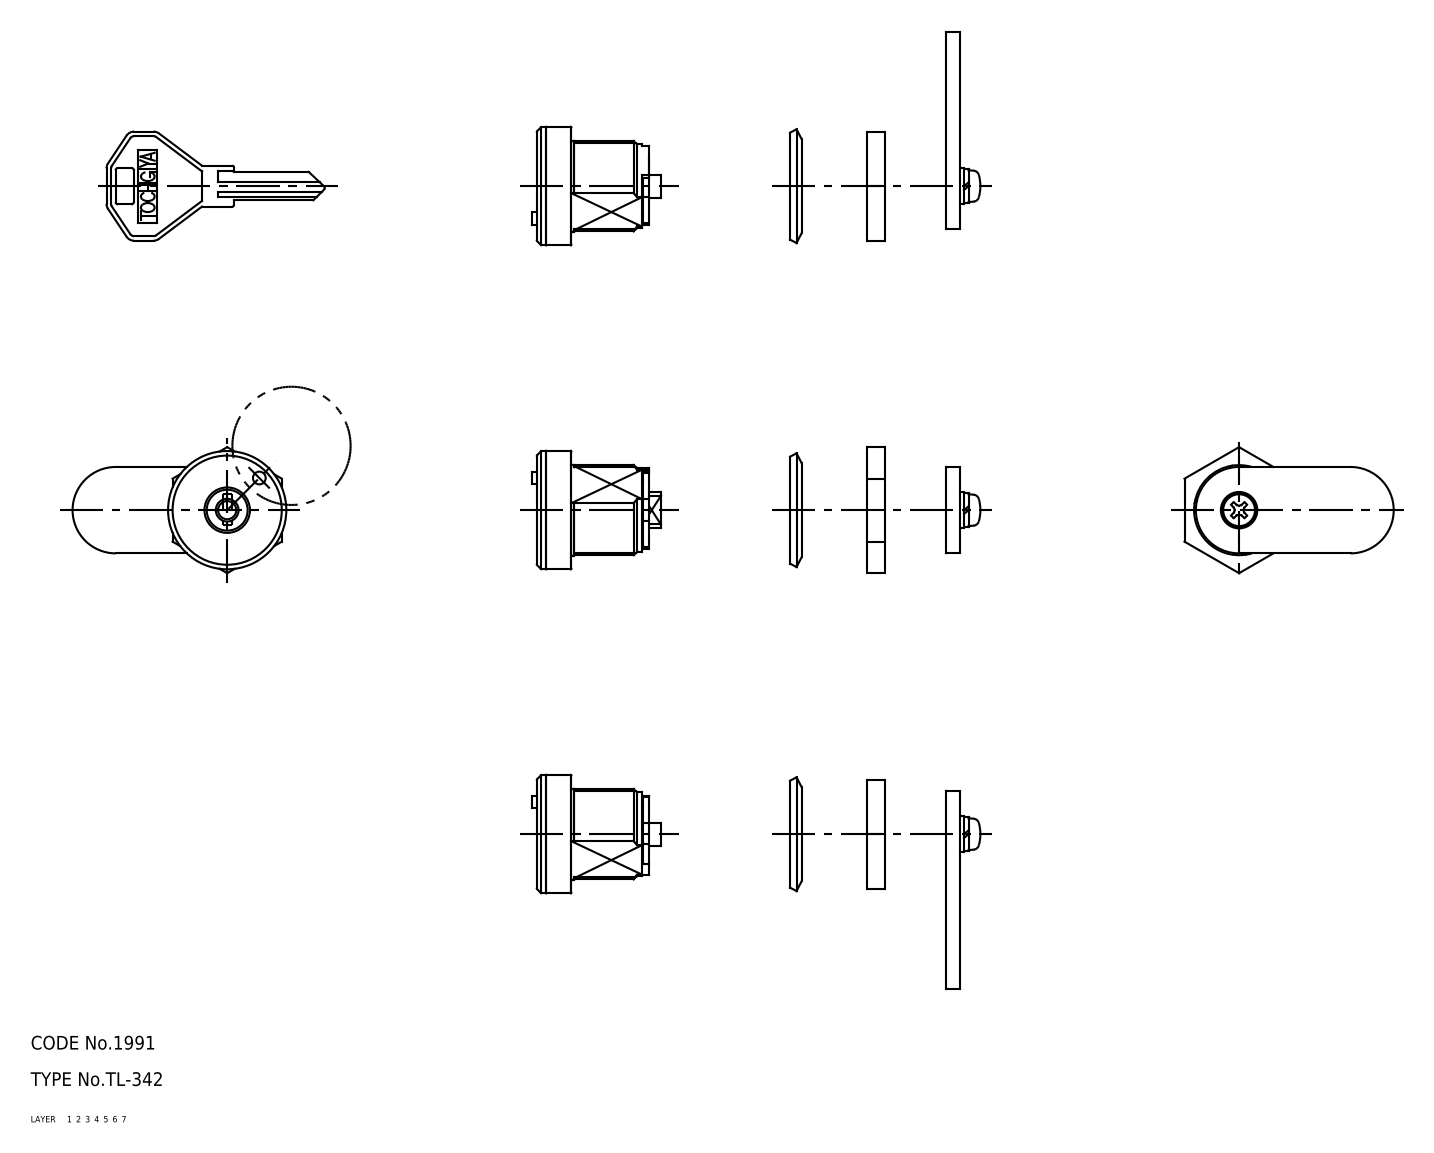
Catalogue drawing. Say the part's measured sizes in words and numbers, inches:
The part is named "washer; screw; nut; lock (+5 more)". Its 3-D file was written by "CADfix (AUTOMOTIVE_DESIGN)". It is 9 solids with 203 faces: 0 planar, 0 cylindrical and 203 other. Overall it measures 4.579 by 1.85 by 1.091 inches. Its volume is 0.764 cubic inches and its surface area 17.57 square inches.
